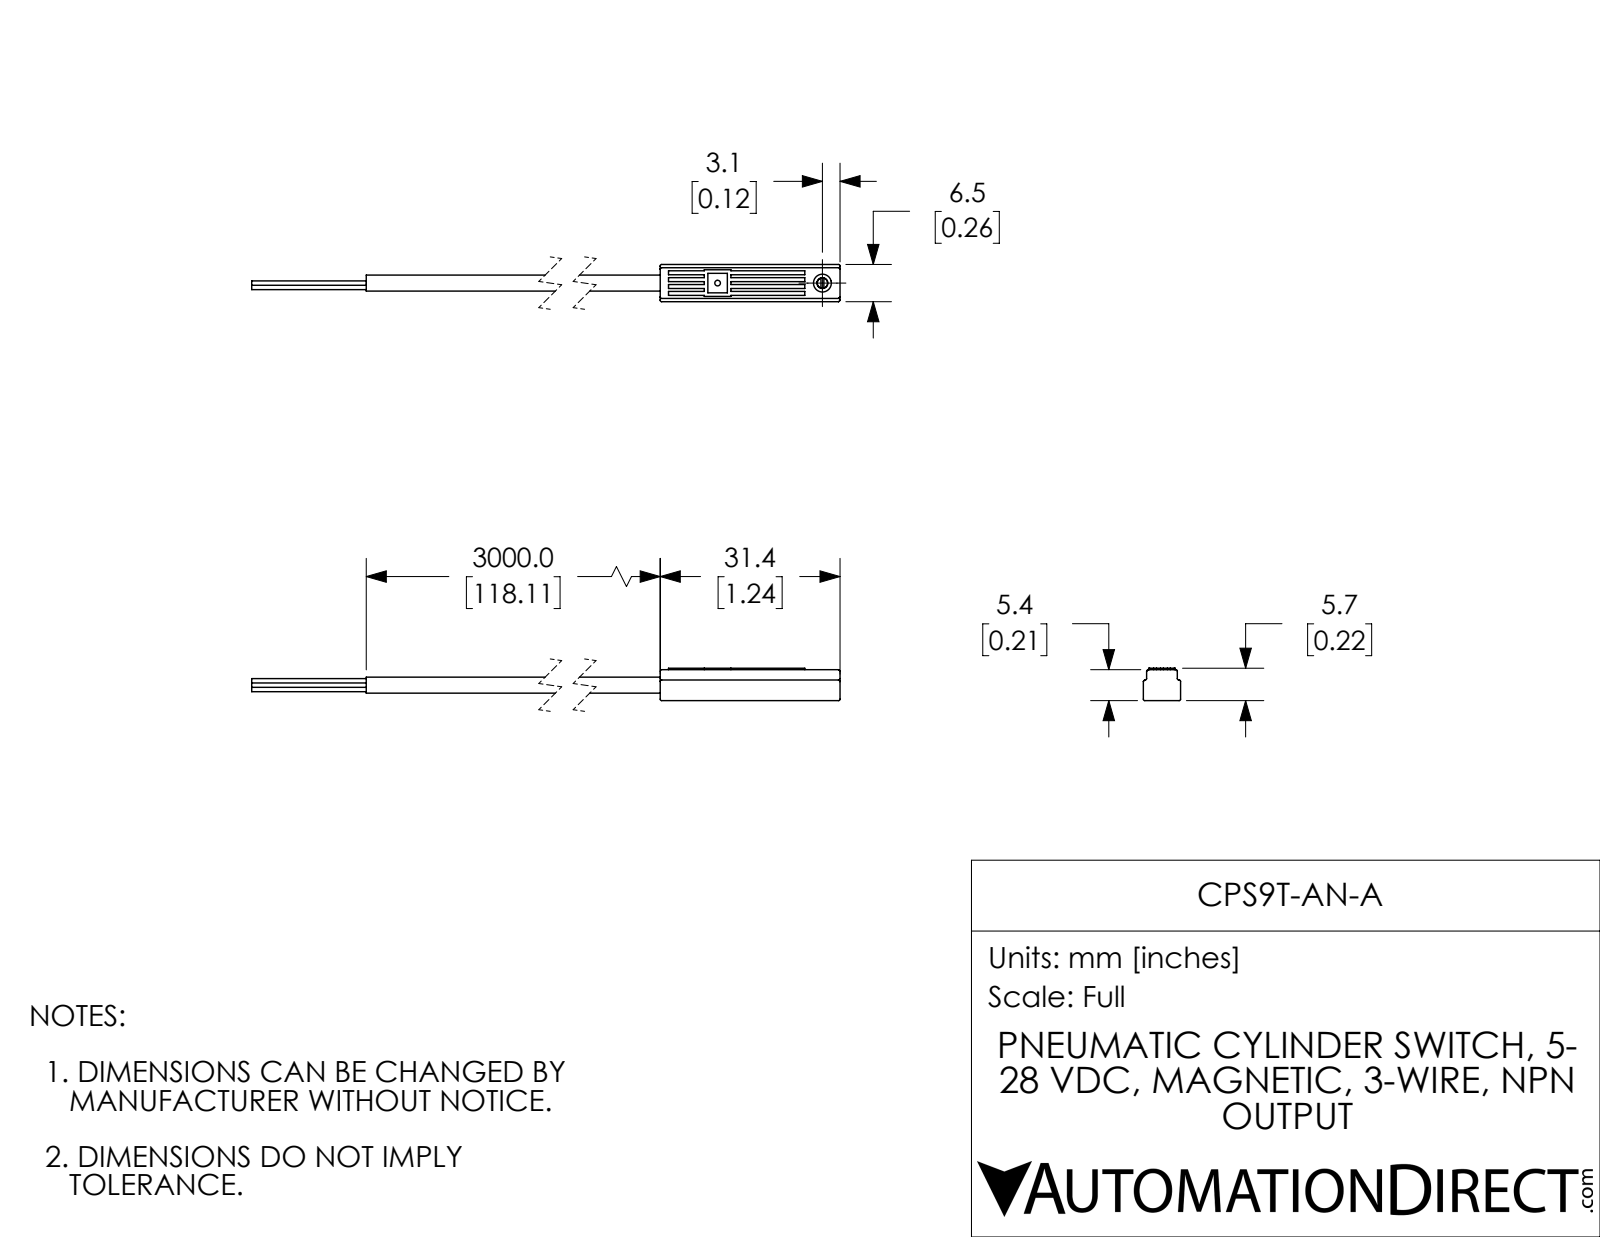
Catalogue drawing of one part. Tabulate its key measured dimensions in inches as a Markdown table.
| quantity | value |
| --- | --- |
| part name | CPS9T-AN-A |
| STEP written by | SolidWorks 2017 (AUTOMOTIVE_DESIGN) |
| units | inches |
| bodies | 2 solids, 127 faces (61 planar, 34 cylindrical, 32 other) |
| overall size | 5.826 × 0.256 × 0.223 |
| volume | 0.107 in³ |
| surface area | 2.968 in² |
| round holes (diameter × count) | 0.075 × 1, 0.123 × 1 |
| round bosses / shafts (diameter × count) | 0.11 × 1, 0.071 × 1 |
| partial cylindrical surfaces (radius × count) | 0.01 × 22 |
| main face-to-face distances | 0.256, 0.022, 0.233, 0.213, 0.222, 0.211, 0.047, 1.236, 0.094, 0.028 |
